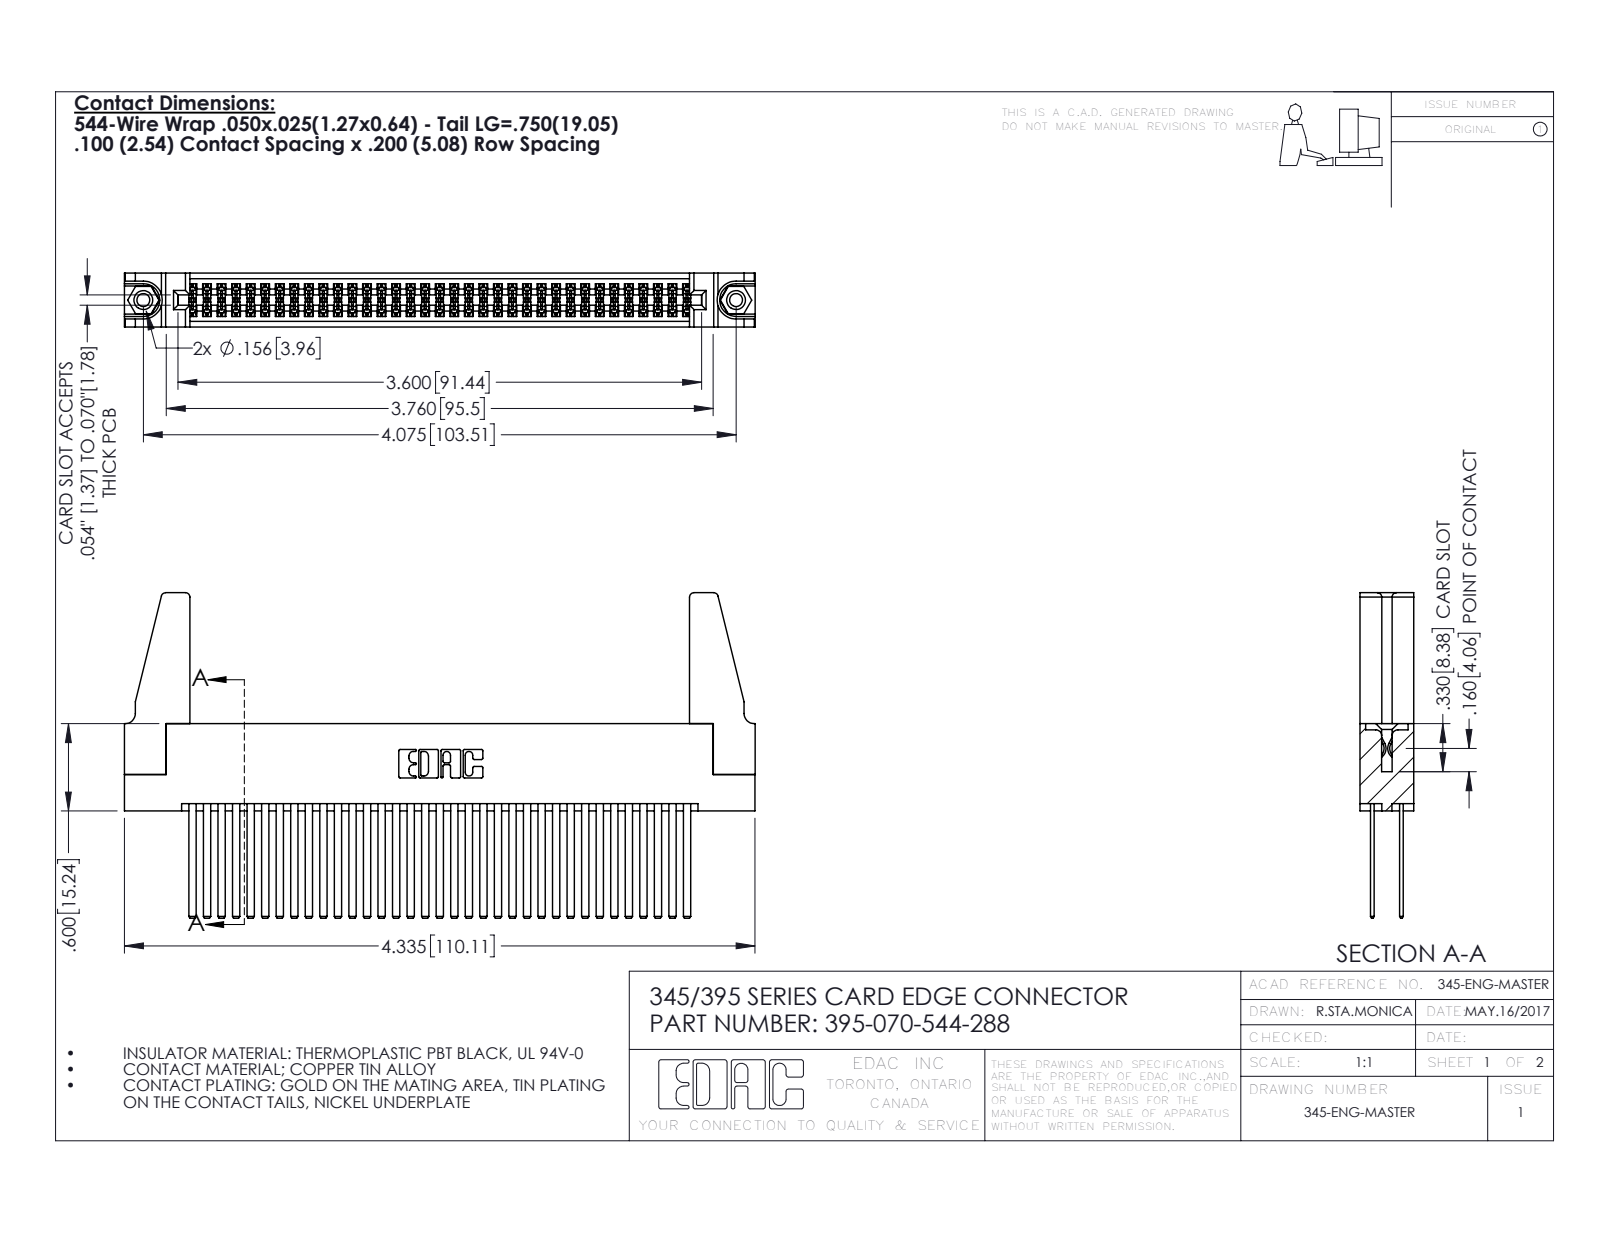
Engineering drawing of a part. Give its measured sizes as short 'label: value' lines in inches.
name: 345-250-001_345-250-001-102; 345 Part_Flush Mounting Lugs - 0.156 Dia-TH; 395-070-544-288; 345-292-001_345-293-144 (+1 more)
written by: SolidWorks 2016 (CONFIG_CONTROL_DESIGN)
unit: in
bodies: 75 solids, 3330 faces (2182 planar, 1132 cylindrical, 16 other)
size: 4.336 × 2.237 × 0.37
volume: 0.907 in³; area: 35.7 in²
holes: 2× ⌀0.089, 2× ⌀0.125, 2× ⌀0.156, 1× ⌀0.064
bosses: 2× ⌀0.155
rounds: 105× R0.006, 22× R0.01, 8× R0.03, 6× R0.007, 6× R0.031, 3× R0.026, 2× R0.014, 2× R0.019
face distances: 0.072, 0.298, 0.2, 0.098, 0.272, 0.025, 0.225, 0.37, 0.175, 0.05
hole spacings: 0.27, 3.839, 4.075
